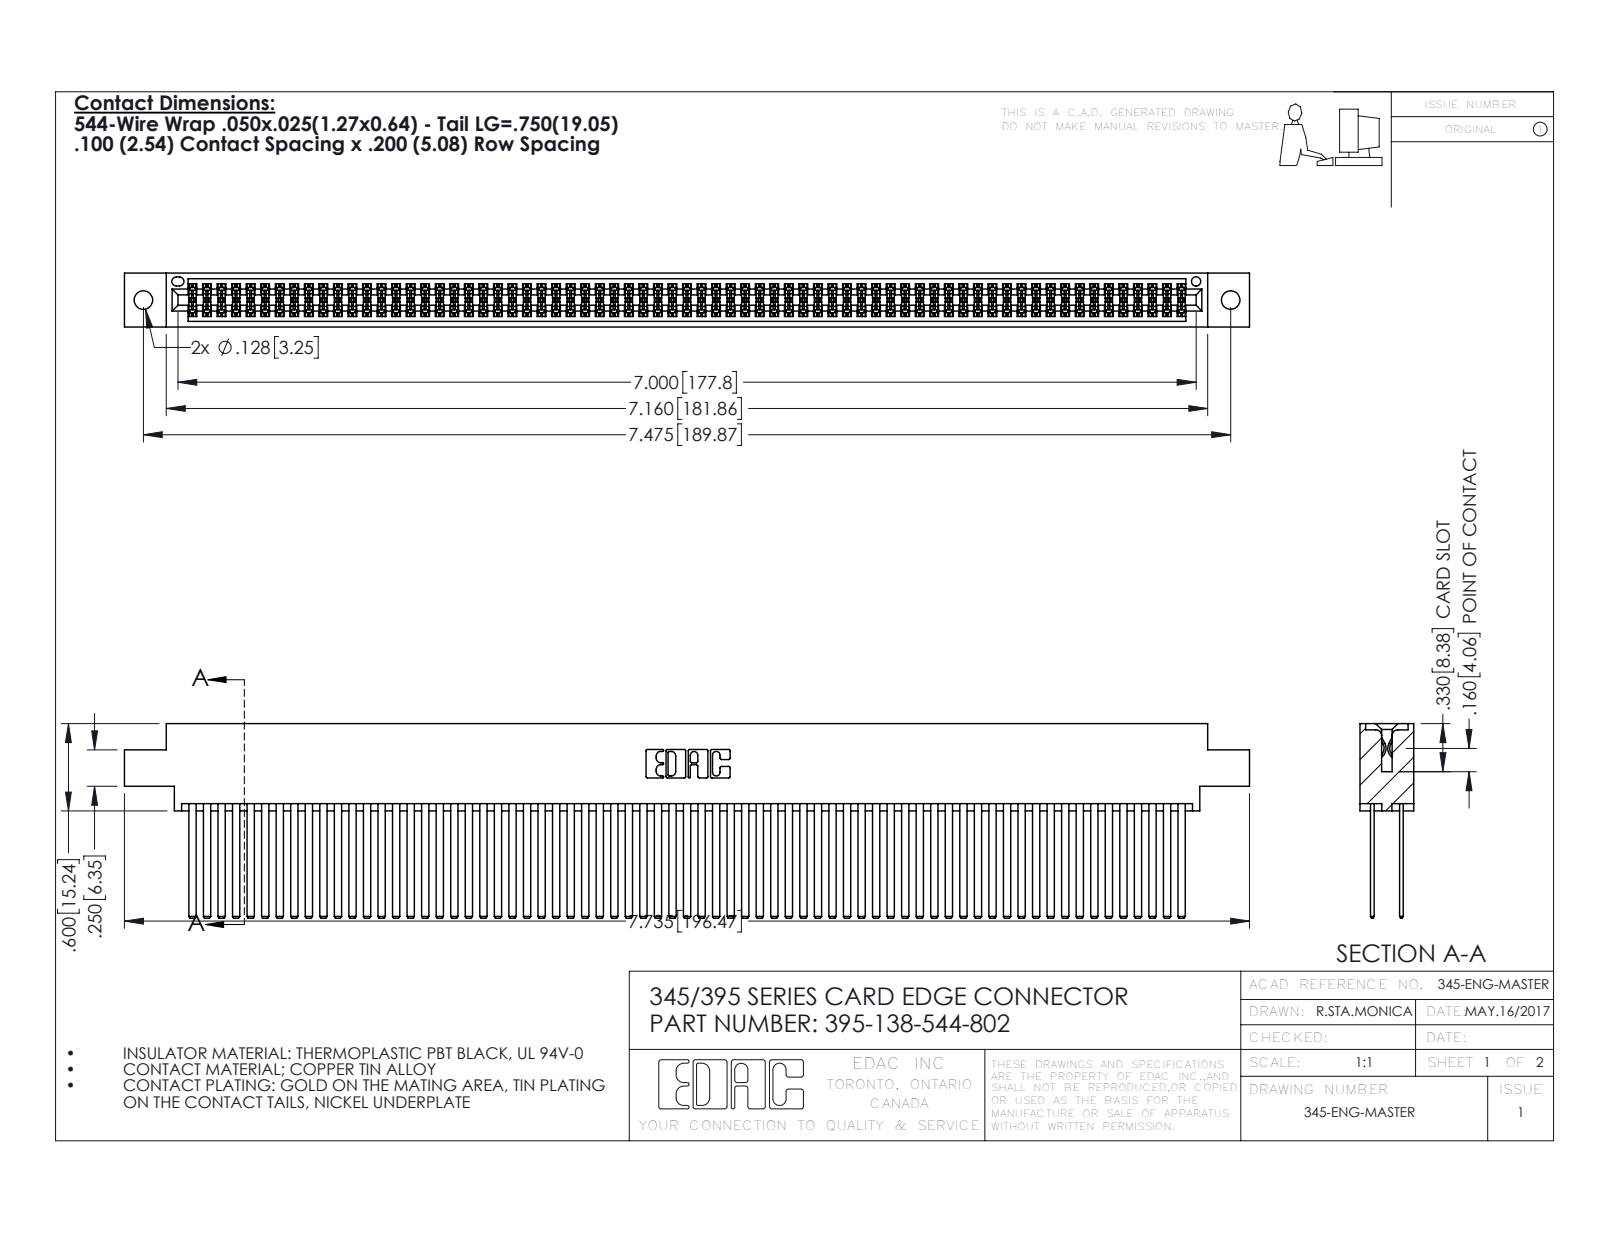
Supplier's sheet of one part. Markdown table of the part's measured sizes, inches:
| quantity | value |
| --- | --- |
| part name | 345-292-001_345-293-144; 395-138-544-802; 345 Part_0.170 Offset - 0.128 Dia |
| STEP written by | SolidWorks 2016 (CONFIG_CONTROL_DESIGN) |
| units | inches |
| bodies | 139 solids, 6202 faces (4086 planar, 2116 cylindrical, 0 other) |
| overall size | 7.735 × 1.337 × 0.37 |
| volume | 1.289 in³ |
| surface area | 57.79 in² |
| round holes (diameter × count) | 0.128 × 2, 0.064 × 1 |
| partial cylindrical surfaces (radius × count) | 0.006 × 207, 0.01 × 22, 0.007 × 6, 0.031 × 6, 0.026 × 3, 0.014 × 2, 0.019 × 2, 0.022 × 2 |
| main face-to-face distances | 0.2, 0.025, 0.298, 0.072, 0.098, 0.272, 0.225, 0.175, 0.37, 0.15 |
| hole center spacings | 0.27, 7.239, 7.475 |
